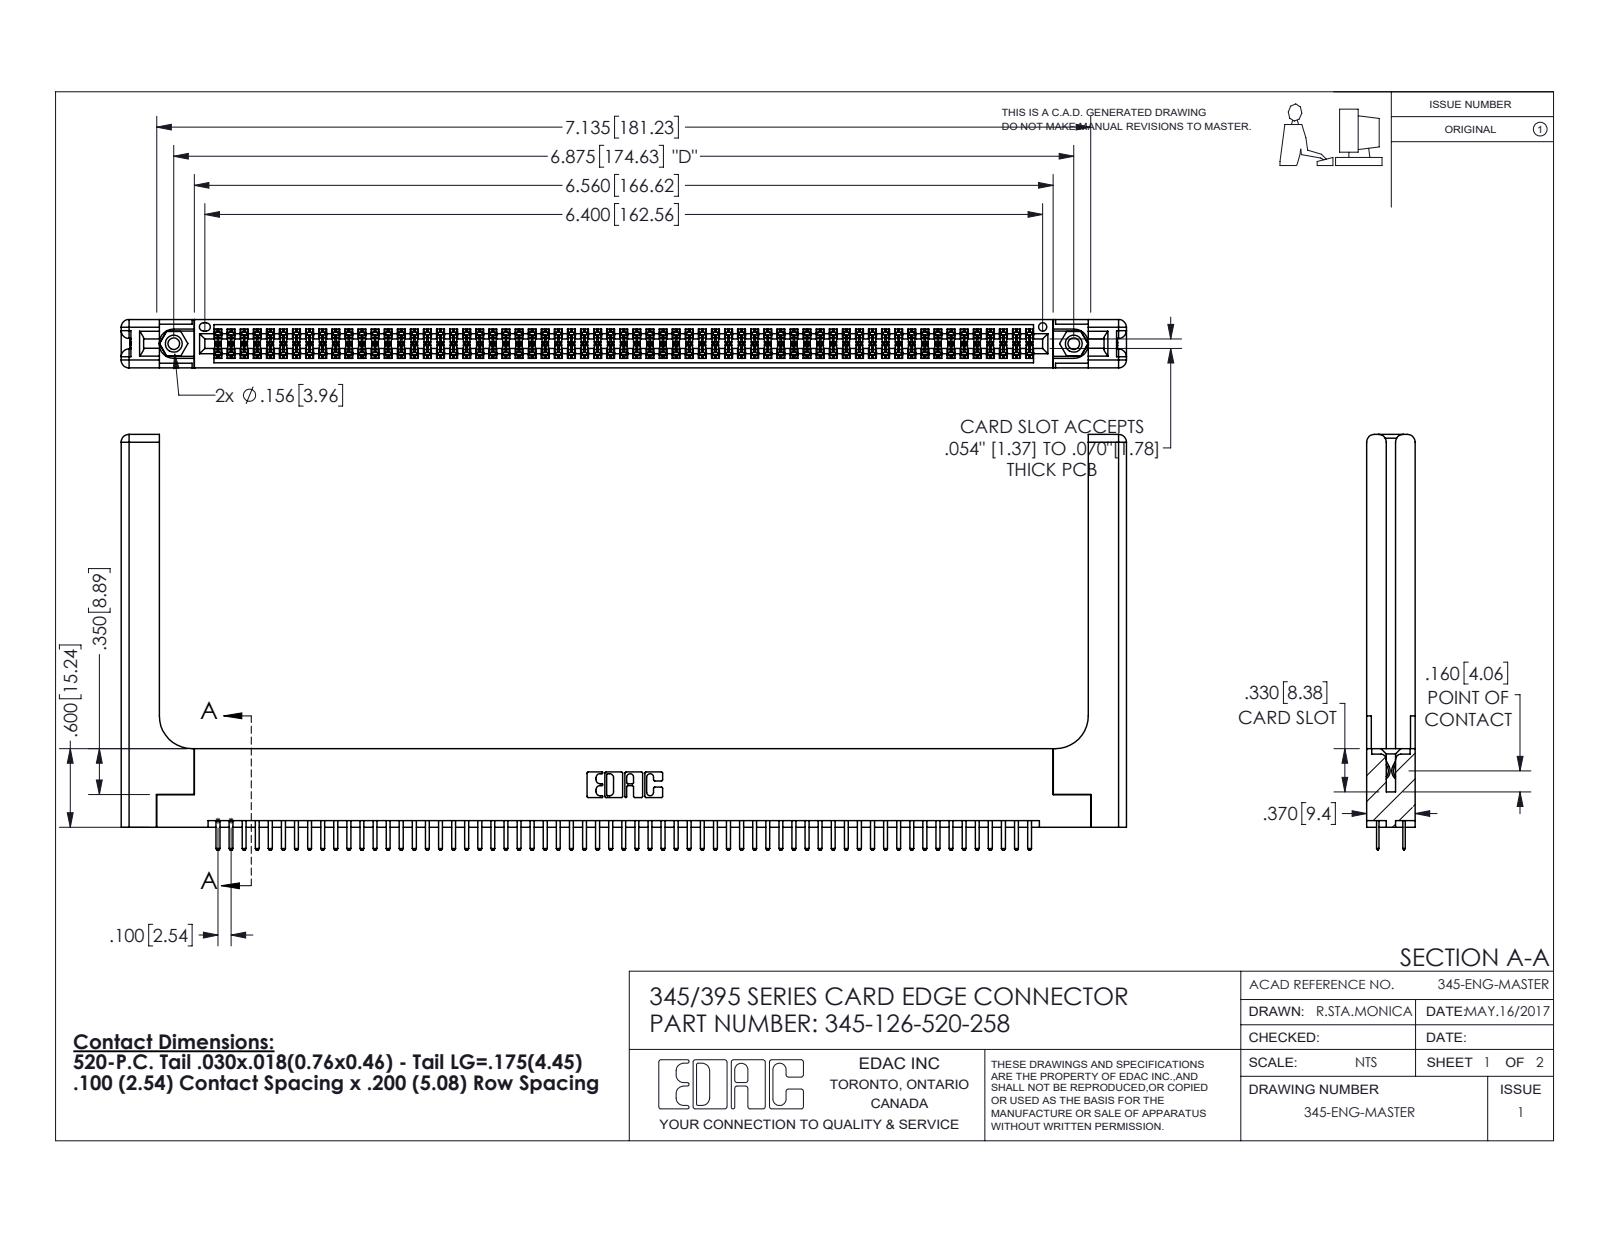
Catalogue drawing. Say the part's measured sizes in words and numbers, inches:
The part is named "345-250-001_345-250-001-102; 345 Part_Flush Mounting Lugs - 0.156 Dia-TH; 345-126-520-258; 345-220-058_345-220-058 (+1 more)". Its 3-D file was written by "SolidWorks 2016 (CONFIG_CONTROL_DESIGN)". It is 131 solids with 7186 faces: 4638 planar, 2488 cylindrical and 60 other. Overall it measures 7.679 by 3.175 by 0.37 inches. Its volume is 1.682 cubic inches and its surface area 52.02 square inches. Round holes: 2 of diameter 0.089, 2 of diameter 0.125, 2 of diameter 0.156, 1 of diameter 0.064. Round bosses or shafts: 2 of diameter 0.155. Partial cylindrical surfaces (rounded edges, fillets, slot ends): 189 of radius 0.006, 130 of radius 0.01, 22 of radius 0.01, 16 of radius 0.06, 6 of radius 0.007, 6 of radius 0.031, 3 of radius 0.026, 2 of radius 0.014. The main face-to-face distances are 0.072, 0.298, 0.37, 0.2, 0.098, 0.272, 0.025, 0.225, 0.022, 0.072. The hole center spacings are 0.27, 6.639, 6.875.
